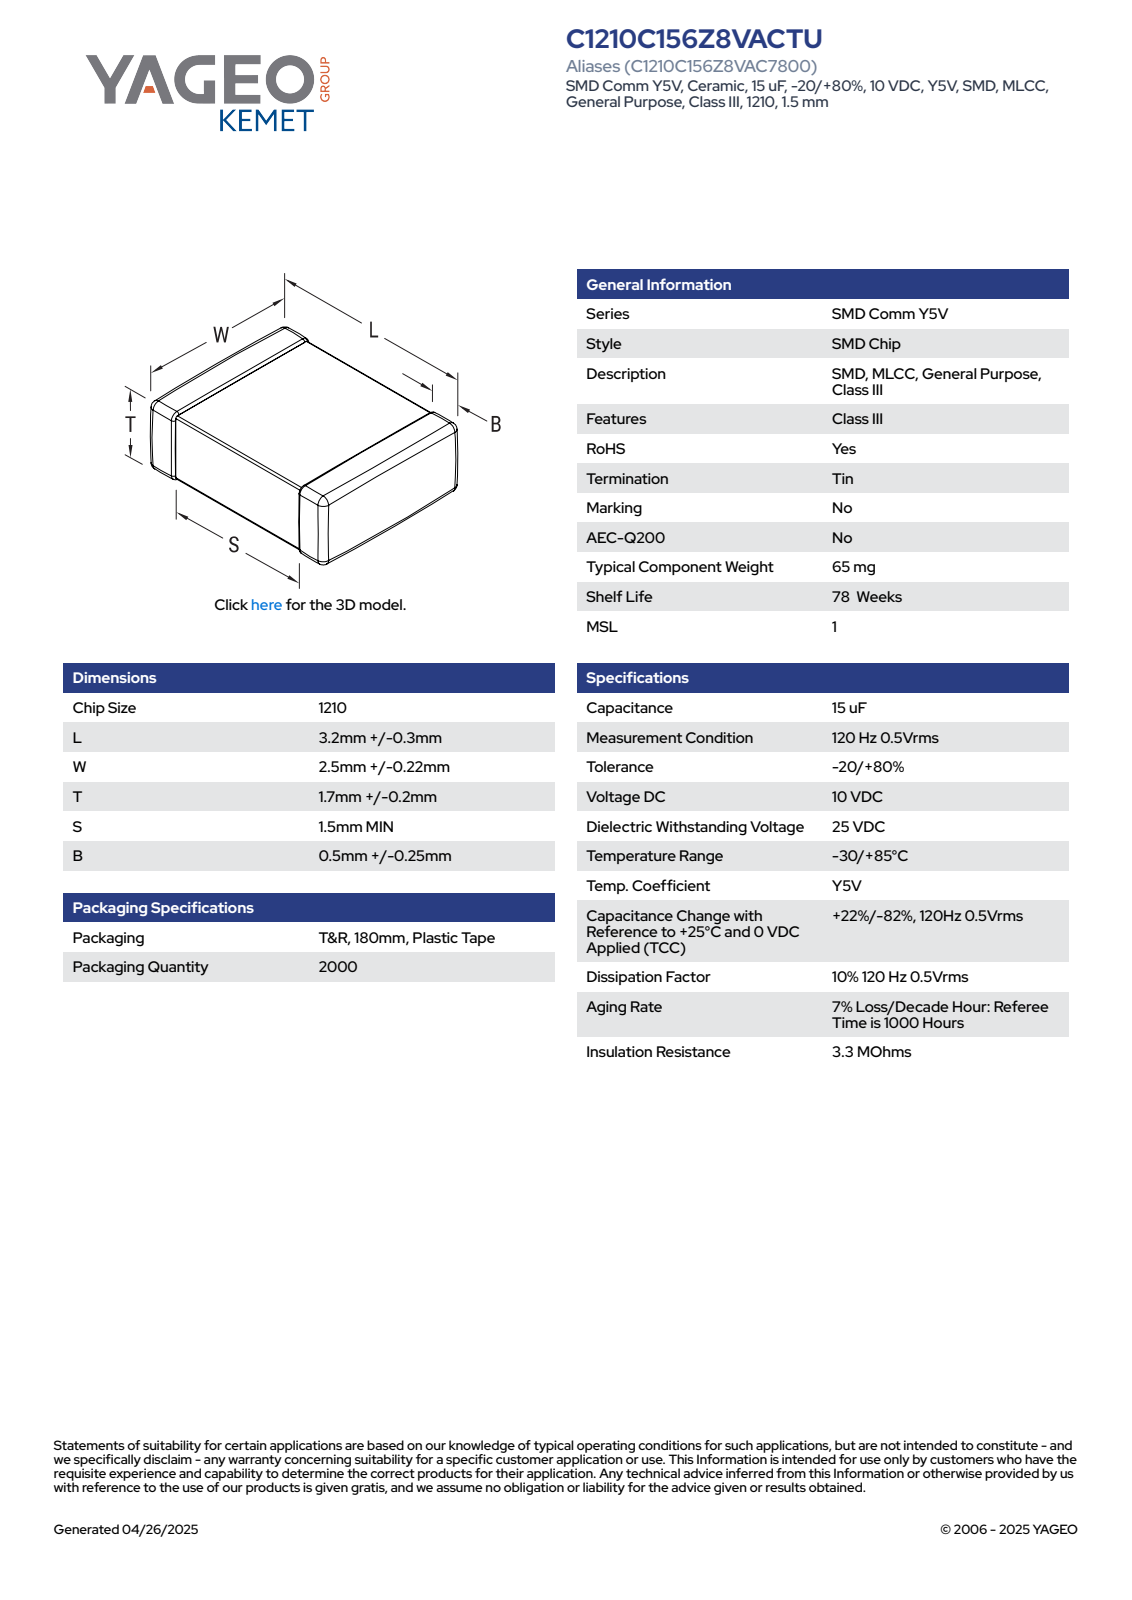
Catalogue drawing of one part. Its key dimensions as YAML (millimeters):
part_name: "CCS_CCSTD_1210_L3.5W2.72T1.9B0.75"
step_written_by: "SolidWorks 2021 (AUTOMOTIVE_DESIGN)"
units: millimeters
bodies: {solids: 4, faces: 125, planar: 71, cylindrical: 38, other: 16}
overall_size: [3.5, 2.72, 1.9]
volume: 17
surface_area: 43
face_to_face_distances: [1.84, 1.78, 3.5, 2.66, 2.6, 1.9, 2.72, 1.79, 1.85, 1.49]
